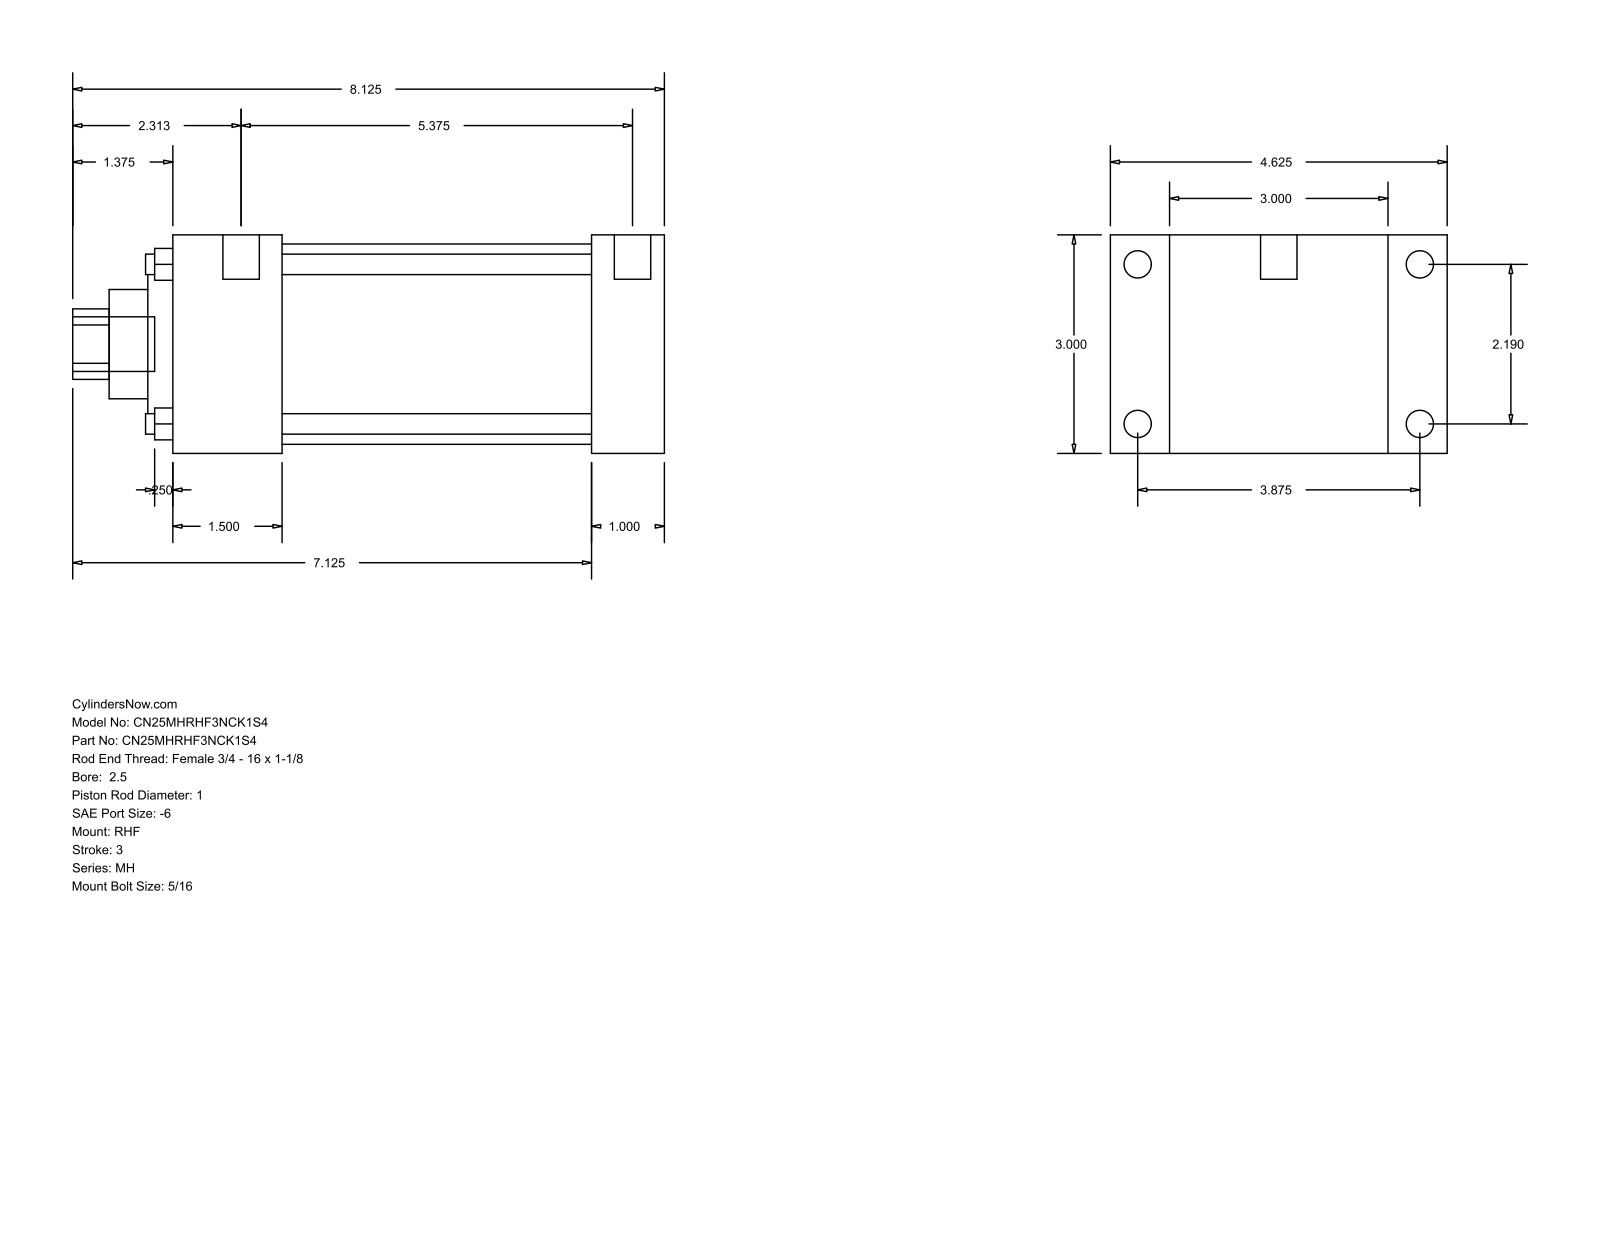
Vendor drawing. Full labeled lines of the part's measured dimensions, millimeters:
Part name (STEP PRODUCT): MH_RHF__0250_1
STEP written by: GSSL Pune (CONFIG_CONTROL_DESIGN)
Units: millimetres
Bodies: 0 solids, 90 faces (61 planar, 29 cylindrical, 0 other)
Overall size (bounding box): 206.38 × 117.47 × 76.2
Round holes (diameter × count): ⌀7.14 ×4, ⌀25.4 ×1, ⌀38.1 ×1, ⌀60.33 ×1, ⌀69.85 ×1
Round bosses / shafts (diameter × count): ⌀9.53 ×4, ⌀5.56 ×4, ⌀12.7 ×2, ⌀19.05 ×1
Partial cylindrical surfaces — rounded edges, fillets, slot ends (radius × count): R12.29 ×1
Main face-to-face distances: 76.2, 25.41, 20.64, 96.84, 146.05, 171.46, 117.48, 38.11, 107.94, 133.35
Hole centre spacings: 39.33, 55.62, 78.66
